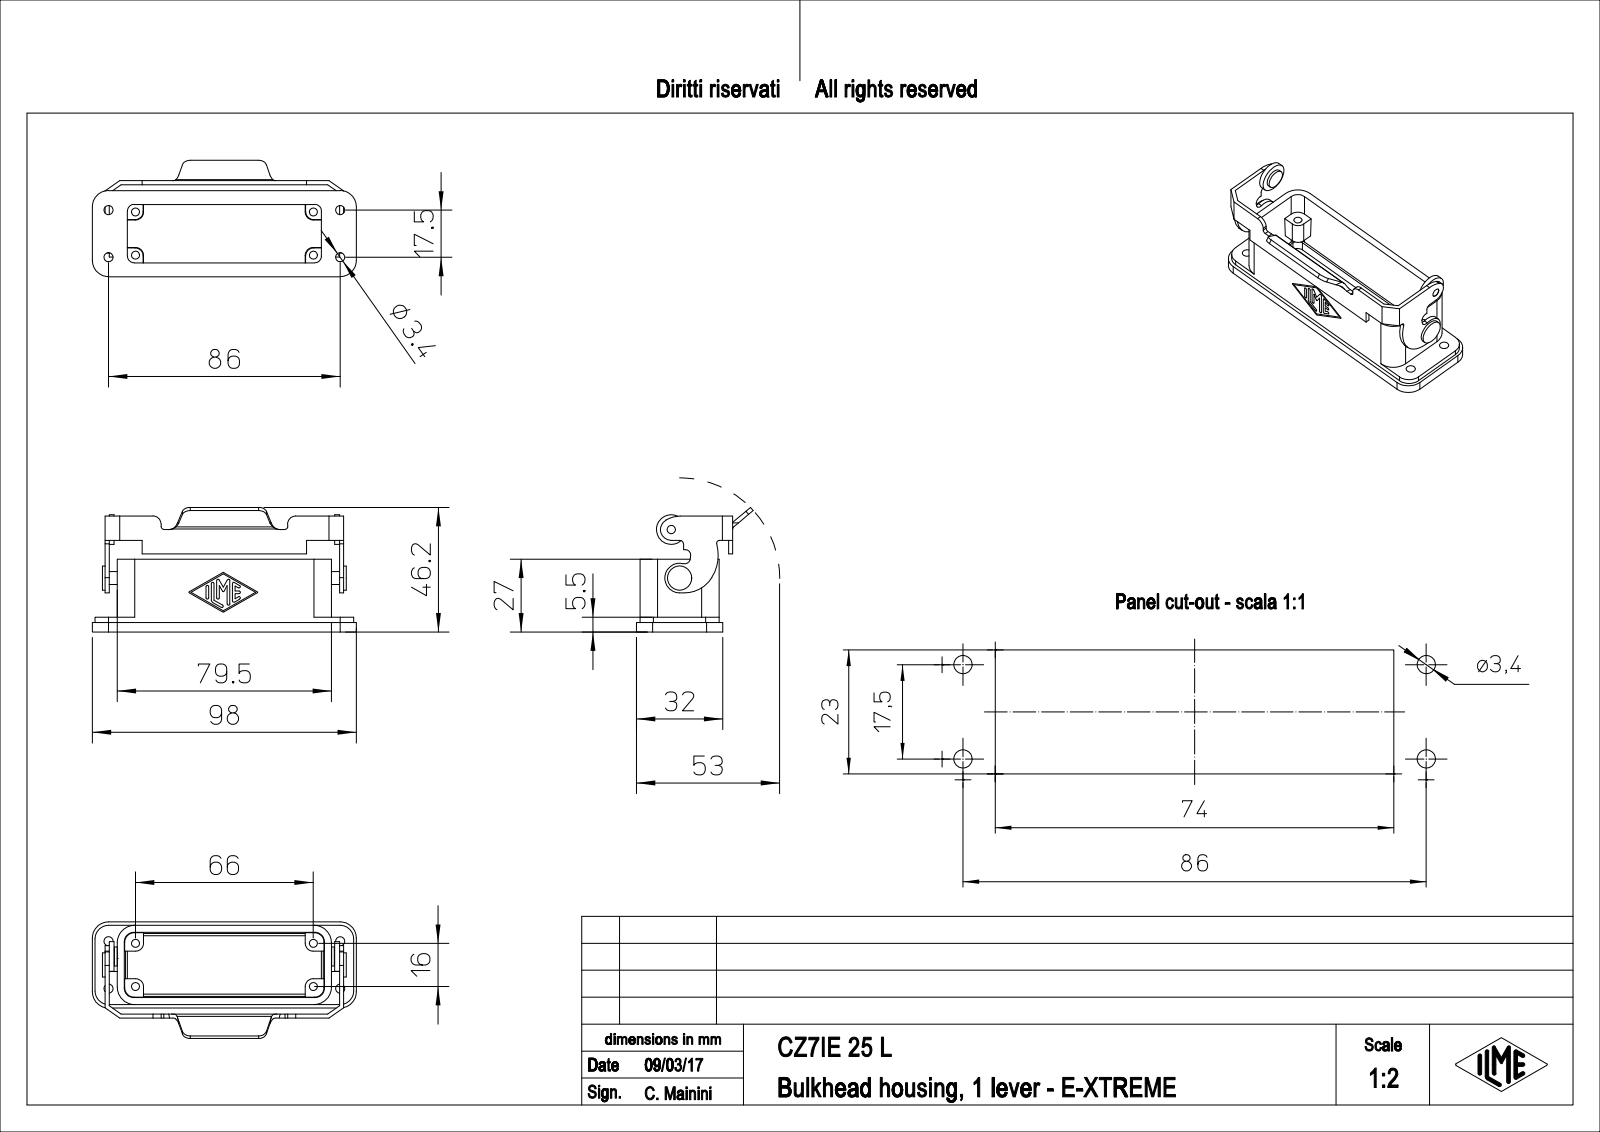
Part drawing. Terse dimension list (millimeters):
name: CZ7IE_25_L
written by: PTC Creo Elements/Direct Modeling 19.0E 27-Jun-2016 (C) Parametric Technology GmbH (AUTOMOTIVE_DESIGN)
unit: mm
bodies: 1 solid, 210 faces (100 planar, 110 cylindrical, 0 other)
size: 98 × 46.2 × 43.28
volume: 24 369 mm³; area: 20 198 mm²
holes: 4× ⌀3, 4× ⌀3.4, 1× ⌀3.1, 1× ⌀5
bosses: 2× ⌀4.8, 1× ⌀11, 1× ⌀9, 1× ⌀7, 1× ⌀3
rounds: 10× R3, 7× R3.5, 5× R2.5, 4× R1, 4× R5, 4× R6, 4× R6.5, 2× R2
face distances: 1.5, 29.4, 3.5, 5, 87, 34.4, 32.9, 84, 5.5, 4.5
hole spacings: 10.03, 19.51, 76, 77.82, 16, 17.5, 66, 67.91
